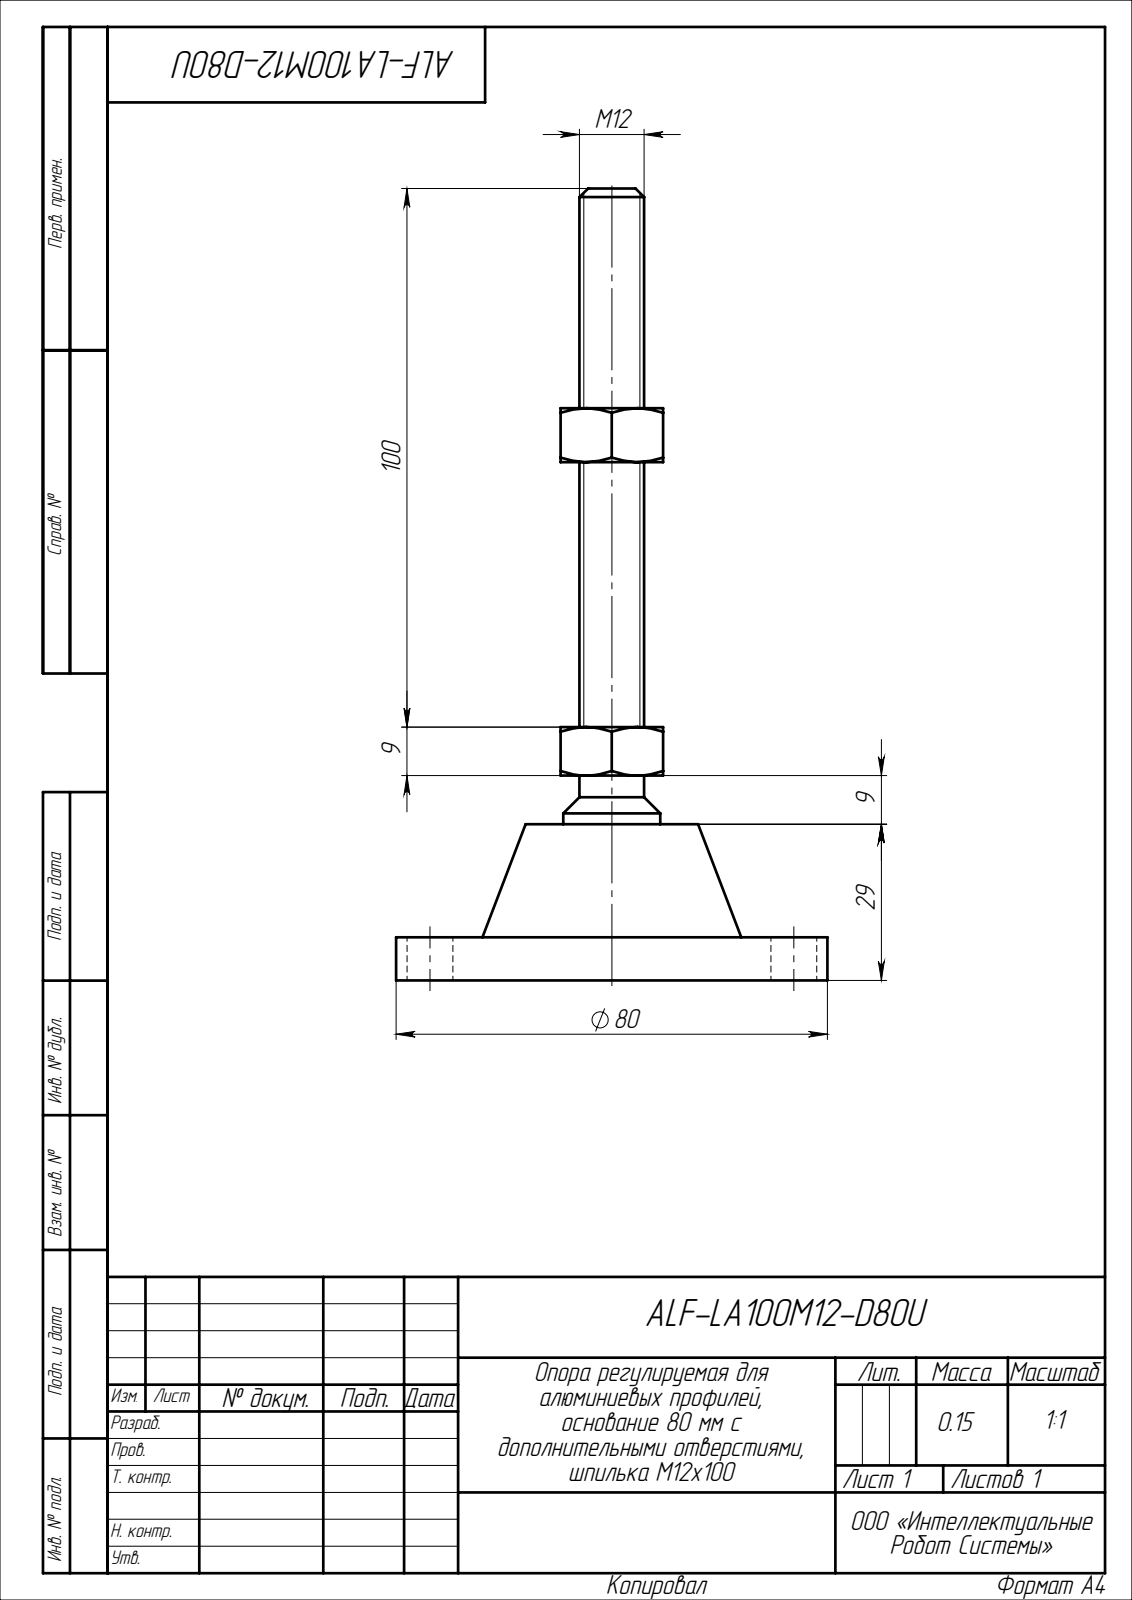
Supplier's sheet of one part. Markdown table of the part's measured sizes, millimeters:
| quantity | value |
| --- | --- |
| part name | ALF-LA100M12-D80U |
| STEP written by | SolidWorks 2022 (CONFIG_CONTROL_DESIGN) |
| units | millimeters |
| bodies | 1 solid, 64 faces (20 planar, 14 cylindrical, 30 other) |
| overall size | 147 × 80 × 80 |
| volume | 83 589 mm³ |
| surface area | 19 749 mm² |
| round holes (diameter × count) | 8.5 × 2 |
| round bosses / shafts (diameter × count) | 80 × 1, 18 × 1, 12 × 1 |
| main face-to-face distances | 8, 19, 29, 21, 9, 38, 30, 47, 39, 18 |
| hole center spacings | 67.5 |
